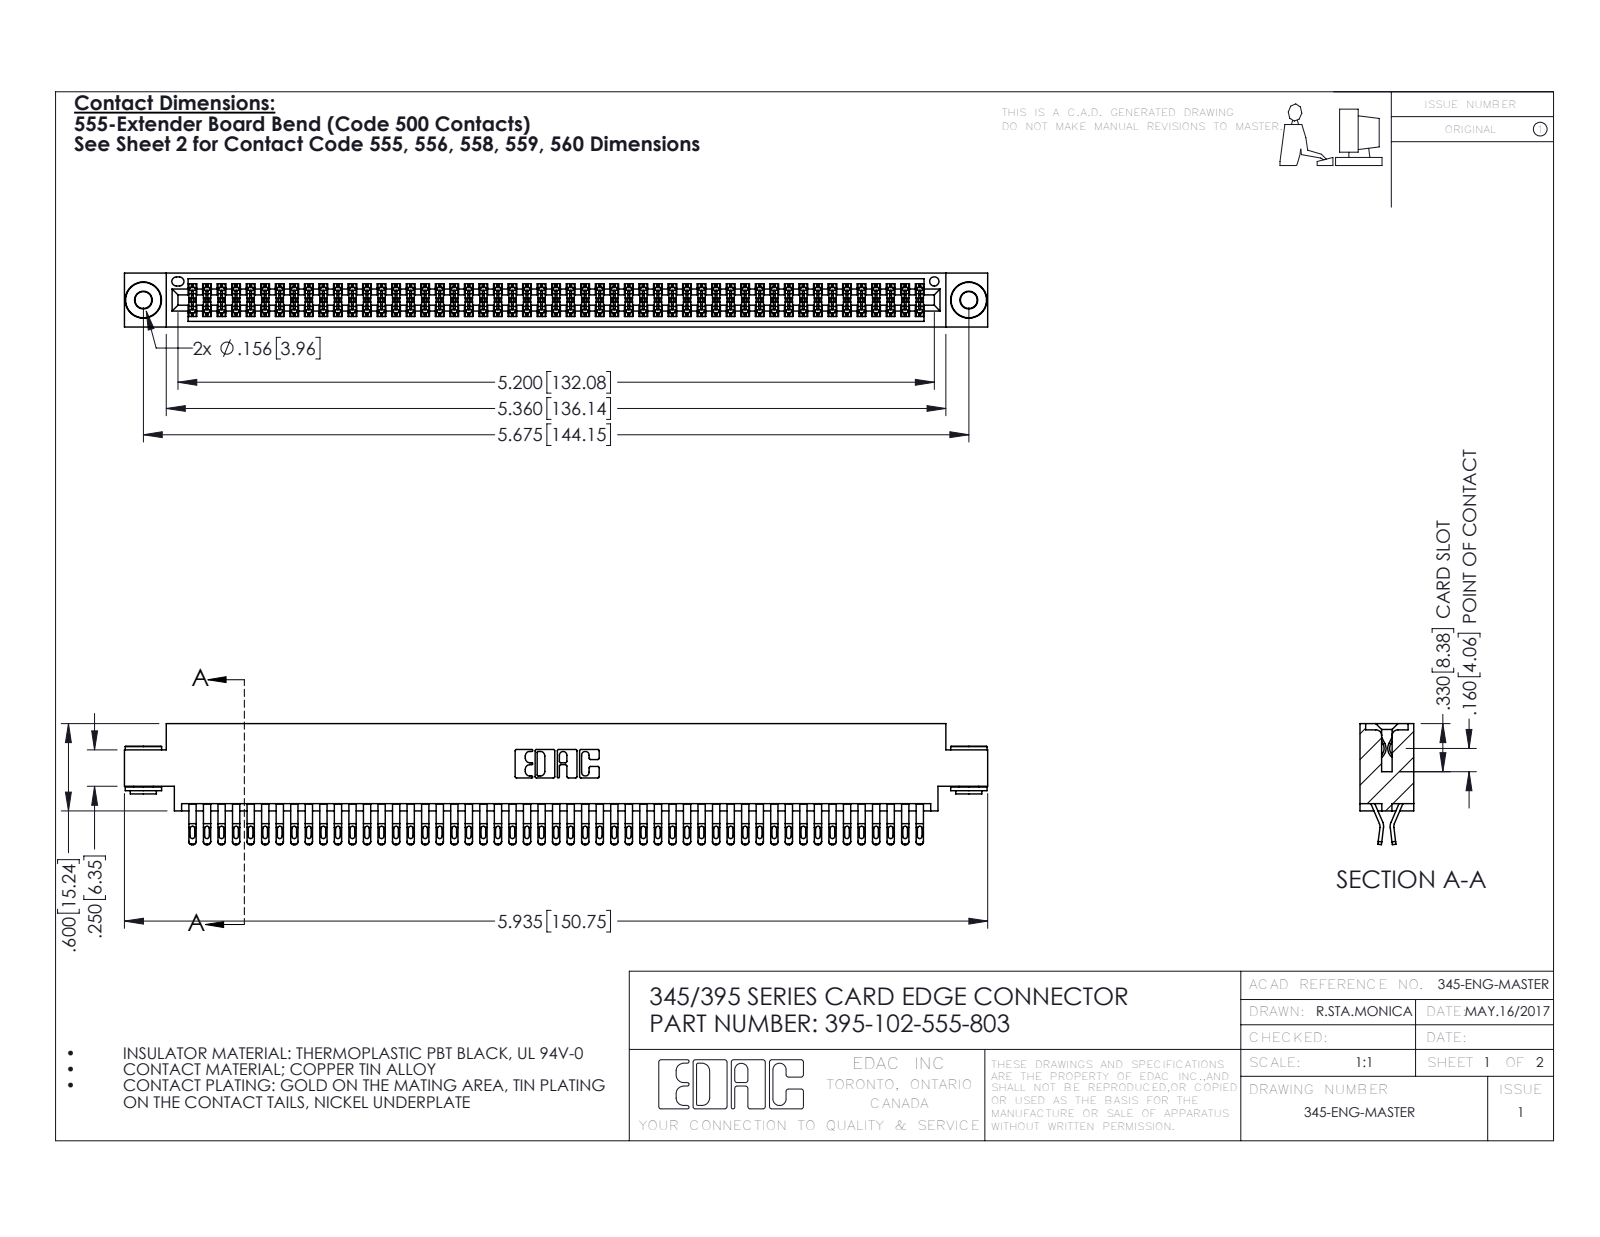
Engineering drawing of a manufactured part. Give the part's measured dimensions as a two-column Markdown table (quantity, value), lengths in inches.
| quantity | value |
| --- | --- |
| part name | 395-102-555-803; 345-292-001_555 Tail; 345-250-002_345-250-002-102; 345 Part_0.170 Offset - 0.156 Dia-TH |
| STEP written by | SolidWorks 2016 (CONFIG_CONTROL_DESIGN) |
| units | inches |
| bodies | 105 solids, 5880 faces (3256 planar, 2616 cylindrical, 8 other) |
| overall size | 5.935 × 0.832 × 0.37 |
| volume | 0.911 in³ |
| surface area | 36.61 in² |
| round holes (diameter × count) | 0.116 × 2, 0.156 × 2, 0.064 × 1 |
| round bosses / shafts (diameter × count) | 0.25 × 2, 0.18 × 2, 0.136 × 2 |
| partial cylindrical surfaces (radius × count) | 0.016 × 255, 0.02 × 204, 0.006 × 153, 0.01 × 22, 0.007 × 6, 0.031 × 6, 0.026 × 3, 0.01 × 2 |
| main face-to-face distances | 0.072, 0.298, 0.37, 0.025, 0.2, 0.098, 0.272, 0.225, 0.175, 0.149 |
| hole center spacings | 0.27, 5.439, 5.675 |
